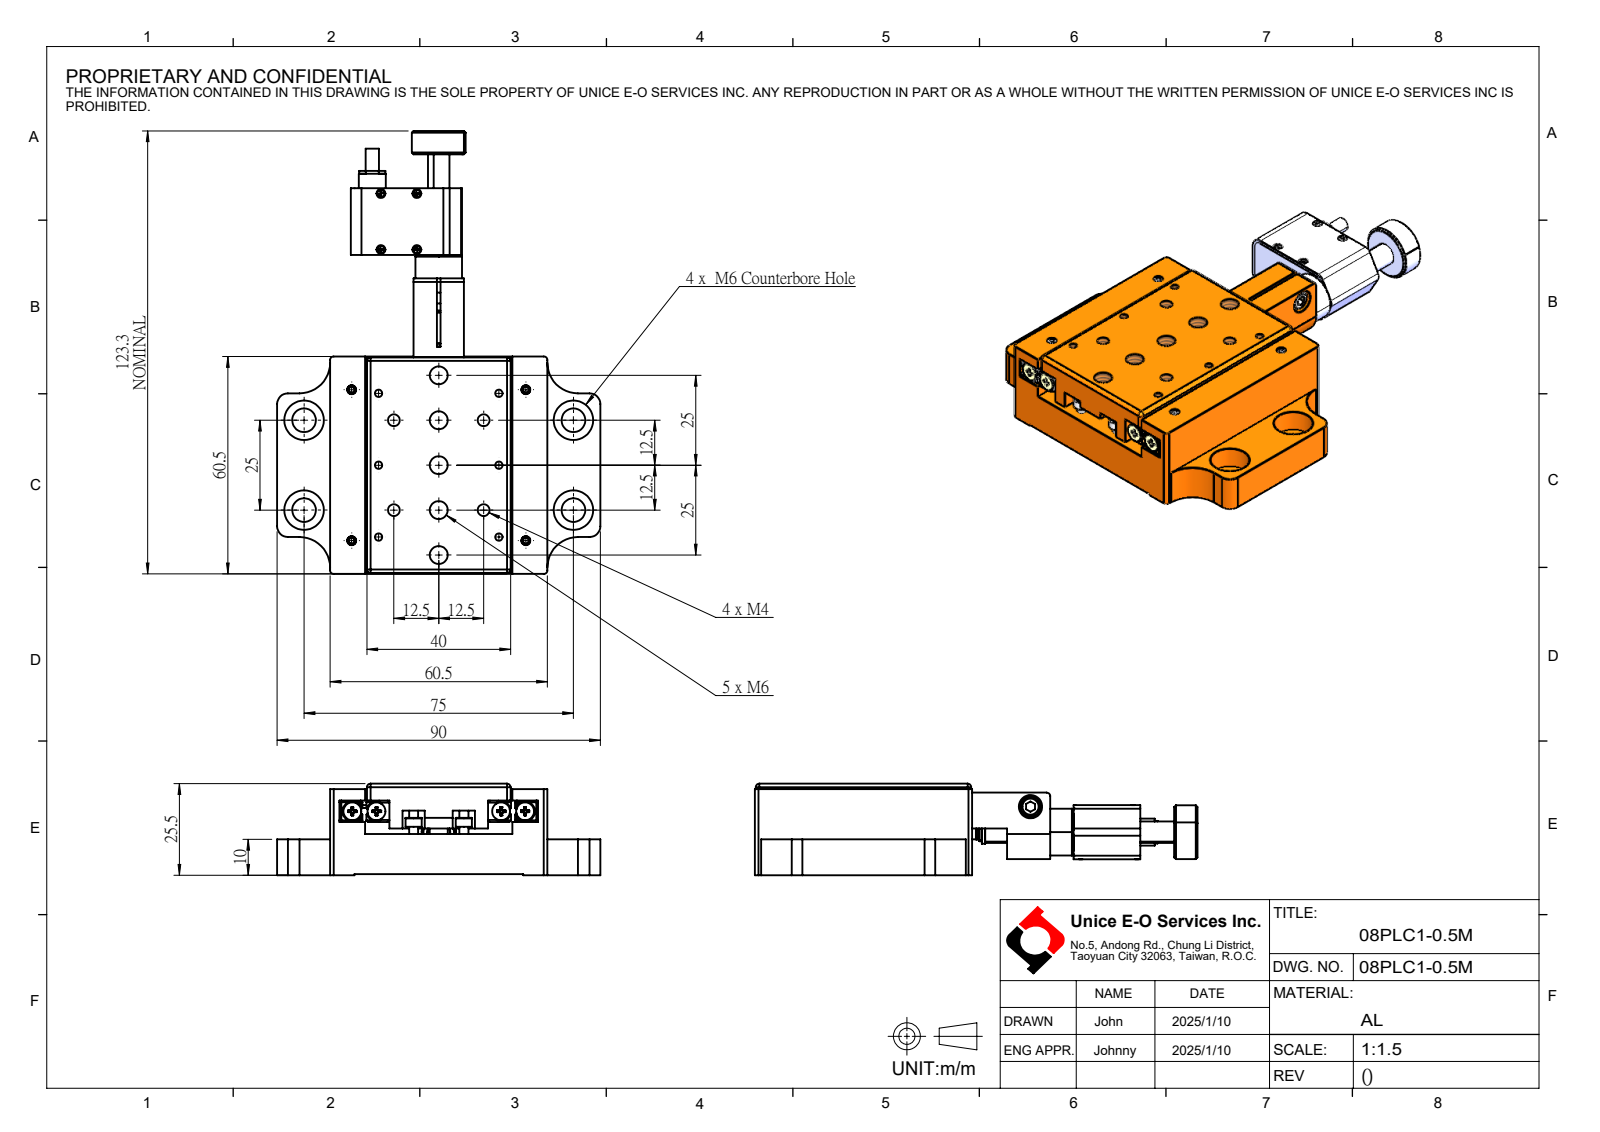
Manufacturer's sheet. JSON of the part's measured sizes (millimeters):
{"part_name": "08PLC1-0.5M", "step_written_by": "SolidWorks 2024 (CONFIG_CONTROL_DESIGN)", "units": "millimeters", "bodies": {"solids": 0, "faces": 692, "planar": 413, "cylindrical": 162, "other": 117}, "overall_size": [123.27, 90, 25.5], "round_holes": [[2.5, 8], [2.05, 6], [5, 5], [3.3, 4], [6.6, 4], [11, 4], [2, 2], [5.6, 1], [6.5, 1], [7.5, 1], [8, 1], [9.5, 1]], "round_bosses_or_shafts": [[5, 5], [4.5, 2], [2.5, 2], [2, 2], [15, 1], [6.4, 1], [6, 1], [5.5, 1]], "partial_cylinders_radius": [[1, 13], [3, 6], [8.5, 4], [2, 3], [7, 1]], "face_to_face_distances": [14, 6, 1.5, 11.2, 11.5, 25.2, 25.5, 3.2, 12.5, 7.5], "hole_center_spacings": [25, 39.53, 12.5, 17.68, 35.36, 37.5, 50, 7.57]}
